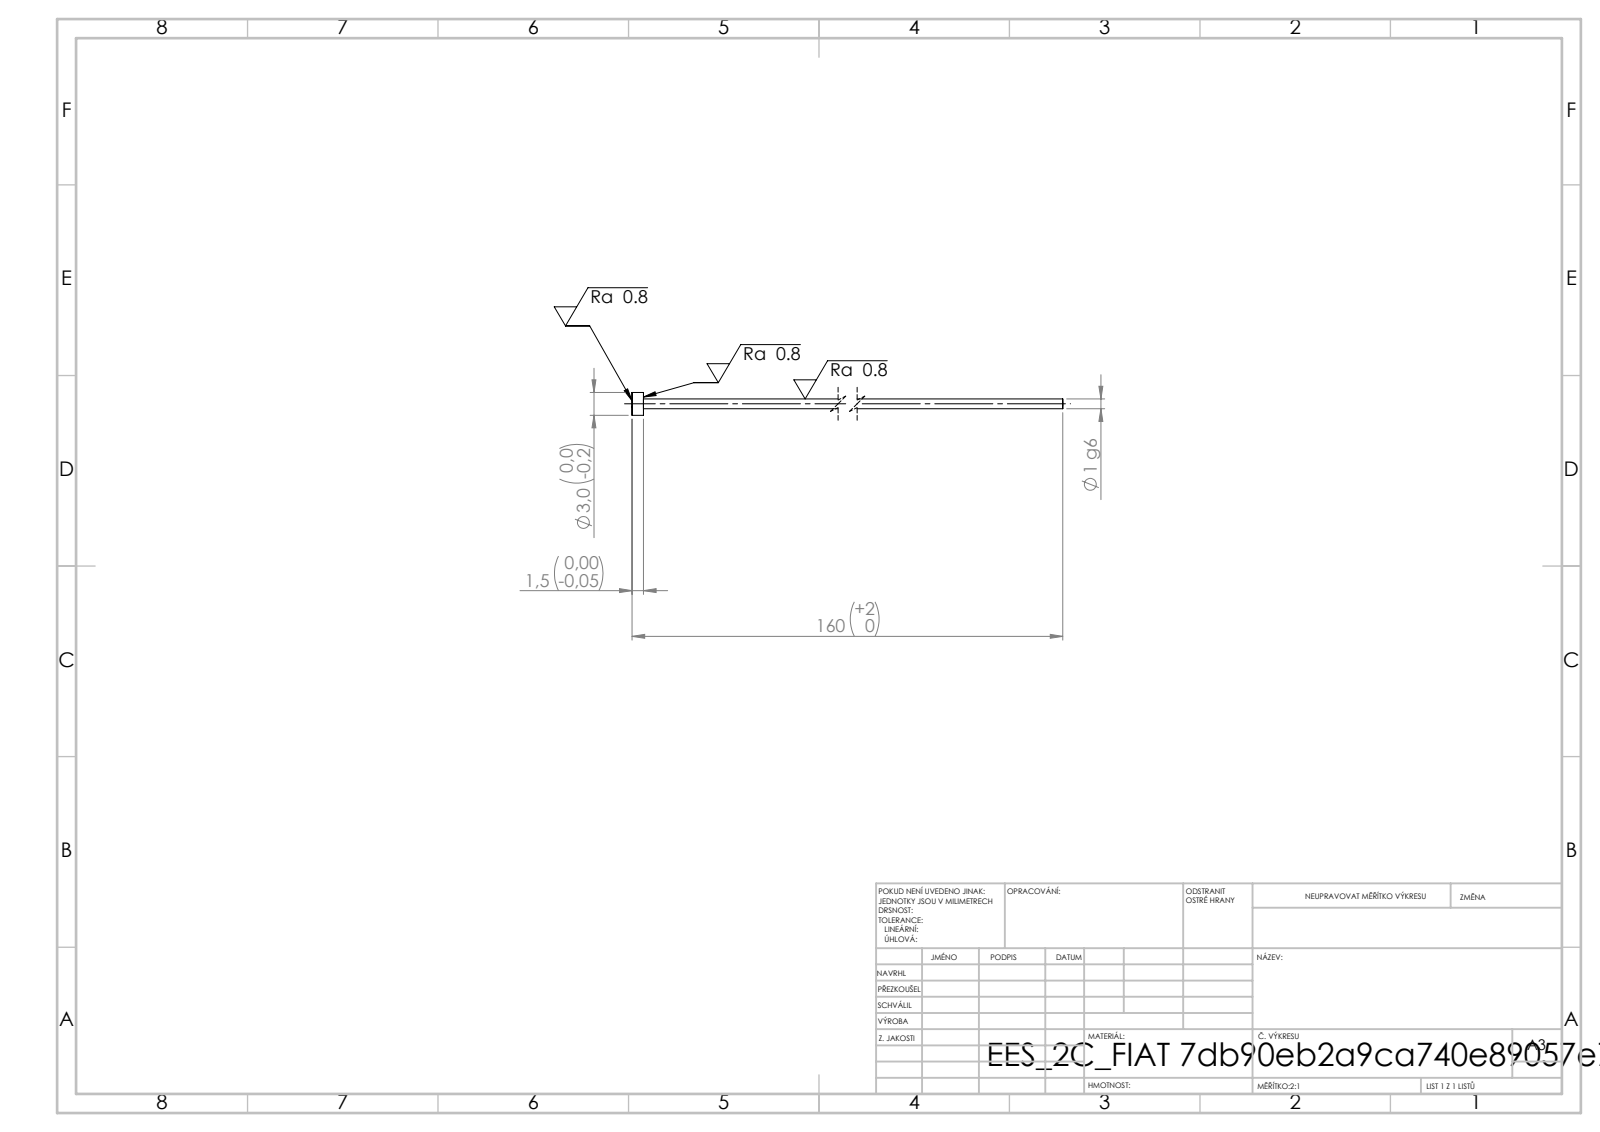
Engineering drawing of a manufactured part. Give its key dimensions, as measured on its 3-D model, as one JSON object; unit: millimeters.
{"step_written_by": "SolidWorks 2019 (CONFIG_CONTROL_DESIGN)", "units": "millimeters", "bodies": {"solids": 1, "faces": 7, "planar": 3, "cylindrical": 4, "other": 0}, "overall_size": [160, 3, 3], "volume_mm3": 221, "surface_area_mm2": 676, "round_bosses_or_shafts": [[3, 1], [1.3, 1]], "face_to_face_distances": [1.5, 160, 158.5]}
